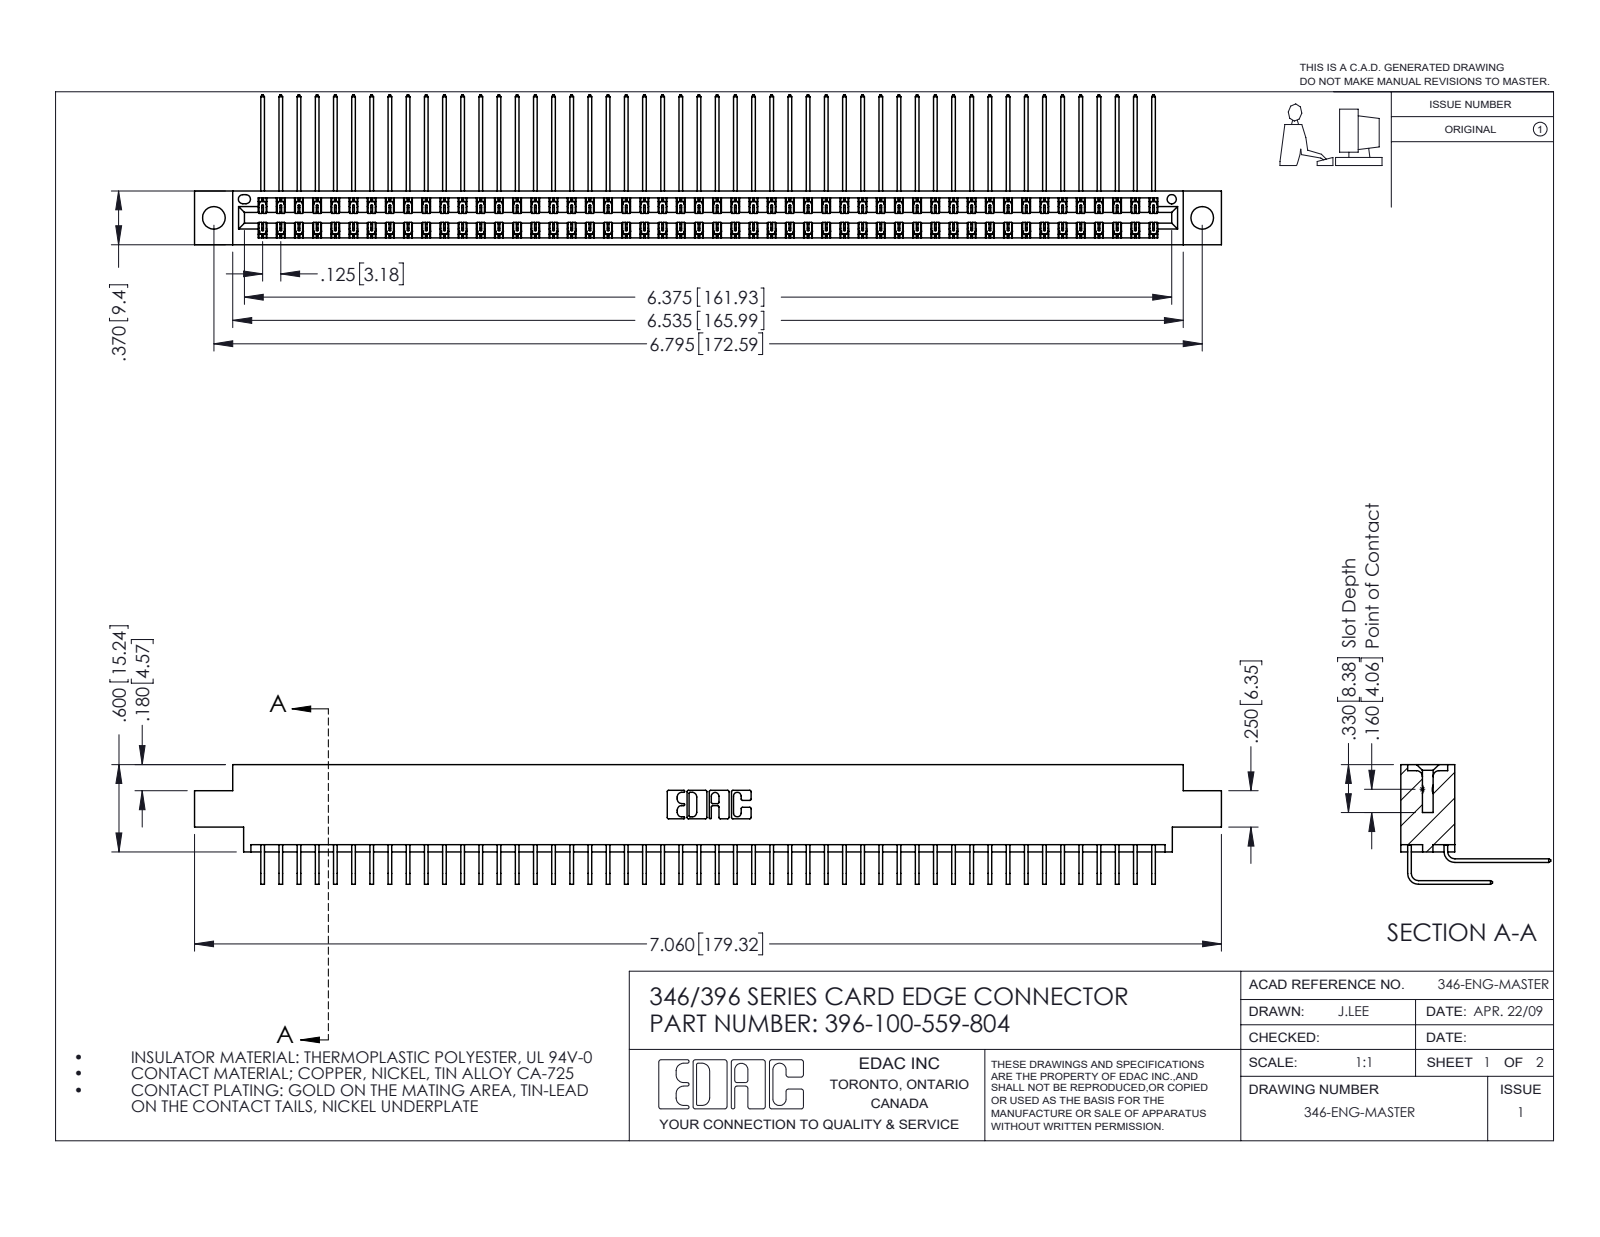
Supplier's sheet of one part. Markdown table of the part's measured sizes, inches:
| quantity | value |
| --- | --- |
| part name | 345-292-001_558 559 Tail - 1; 346 Part_0.170 Offset - 0.156 Dia-TH; 396-100-559-804; 345-292-001_559 Tail - 2 |
| STEP written by | SolidWorks 2016 (CONFIG_CONTROL_DESIGN) |
| units | inches |
| bodies | 101 solids, 5526 faces (3780 planar, 1746 cylindrical, 0 other) |
| overall size | 7.06 × 1.03 × 0.823 |
| volume | 1.091 in³ |
| surface area | 42.57 in² |
| round holes (diameter × count) | 0.156 × 2, 0.064 × 1 |
| partial cylindrical surfaces (radius × count) | 0.006 × 150, 0.01 × 22, 0.007 × 6, 0.031 × 6, 0.026 × 3, 0.014 × 2, 0.022 × 2, 0.024 × 2 |
| main face-to-face distances | 0.048, 0.322, 0.025, 0.37, 0.25, 0.072, 0.298, 0.275, 0.148, 0.222 |
| hole center spacings | 0.246, 6.586, 6.795 |
